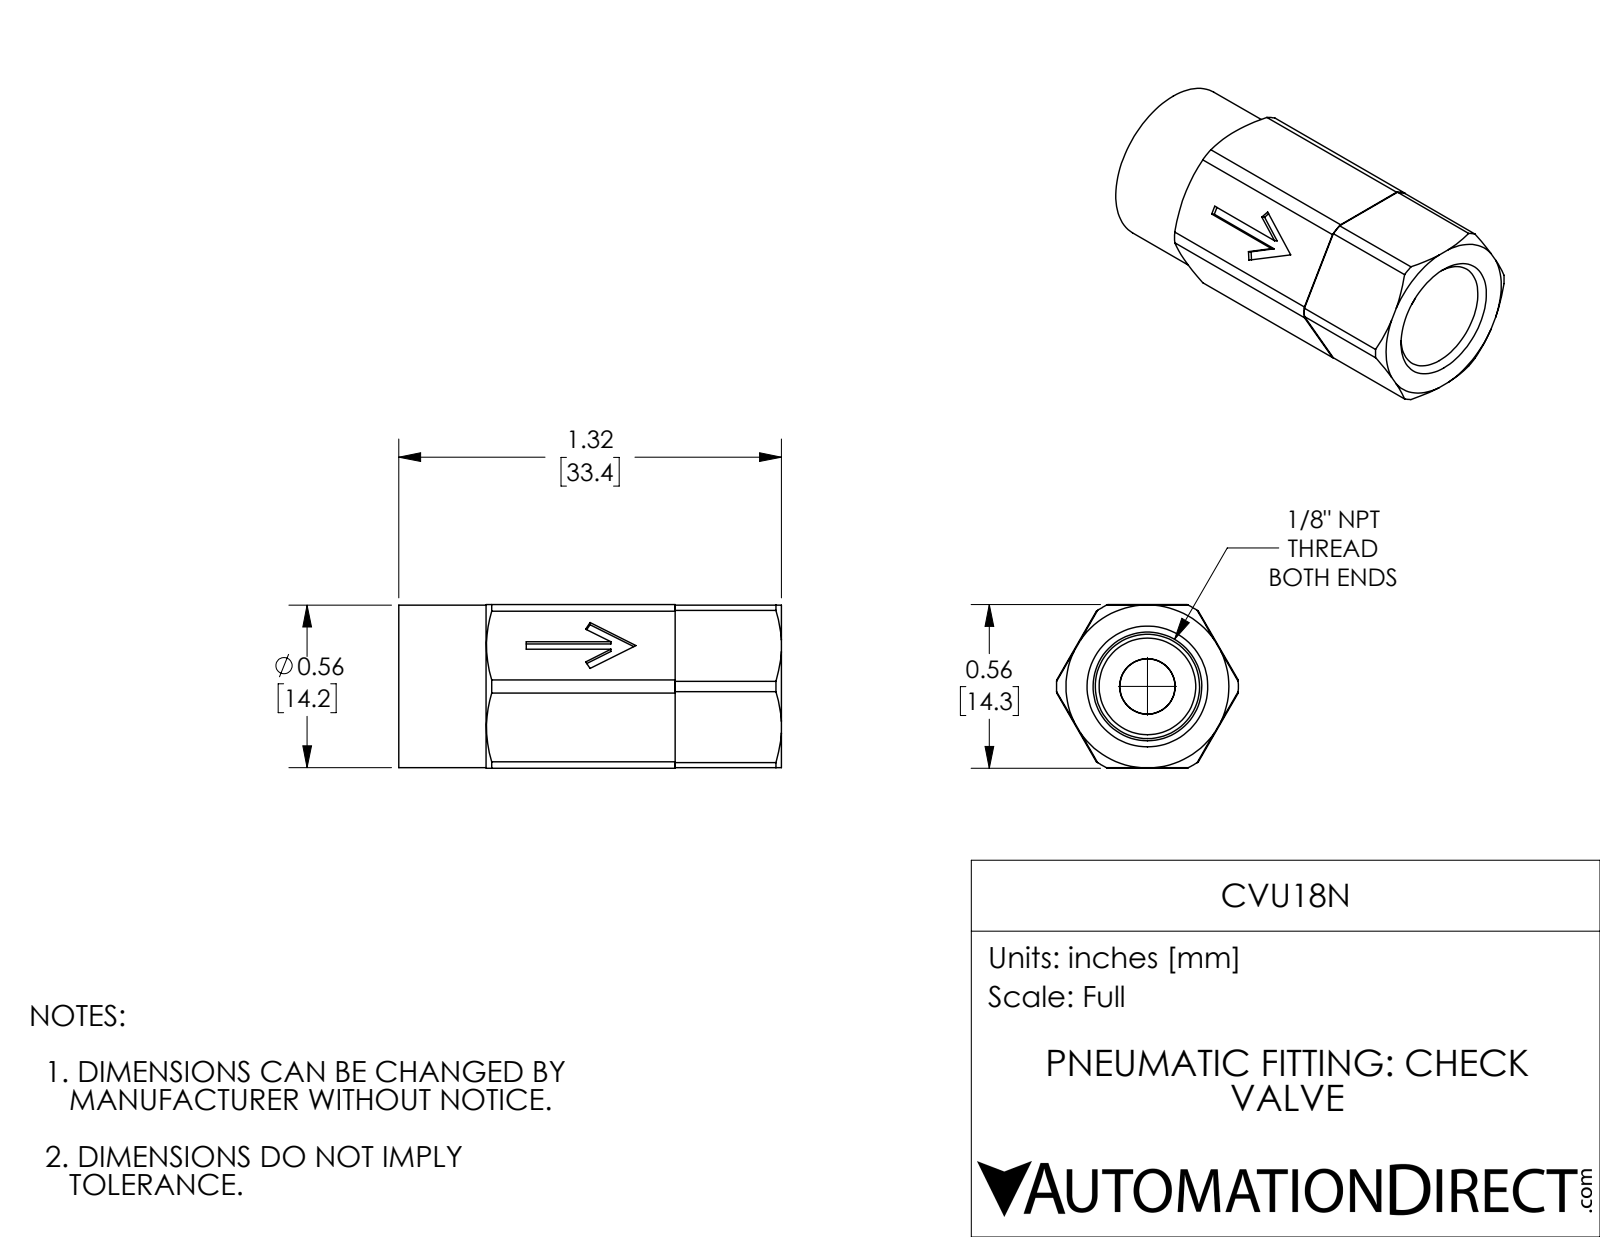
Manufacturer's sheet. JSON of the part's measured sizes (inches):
{"part_name": "CVU18N", "step_written_by": "SolidWorks 2018 (AUTOMOTIVE_DESIGN)", "units": "inches", "bodies": {"solids": 2, "faces": 77, "planar": 33, "cylindrical": 28, "other": 16}, "overall_size": [1.315, 0.625, 0.563], "volume_in3": 0.261, "surface_area_in2": 6.023, "round_holes": [[0.19, 1], [0.191, 1], [0.332, 1], [0.453, 1], [0.536, 1]], "round_bosses_or_shafts": [[0.558, 1], [0.5, 1]], "partial_cylinders_radius": [[0.313, 1]], "face_to_face_distances": [0.56, 0.562, 0.558, 0.075, 0.545, 0.47, 0.35, 0.965, 0.91, 0.835]}
